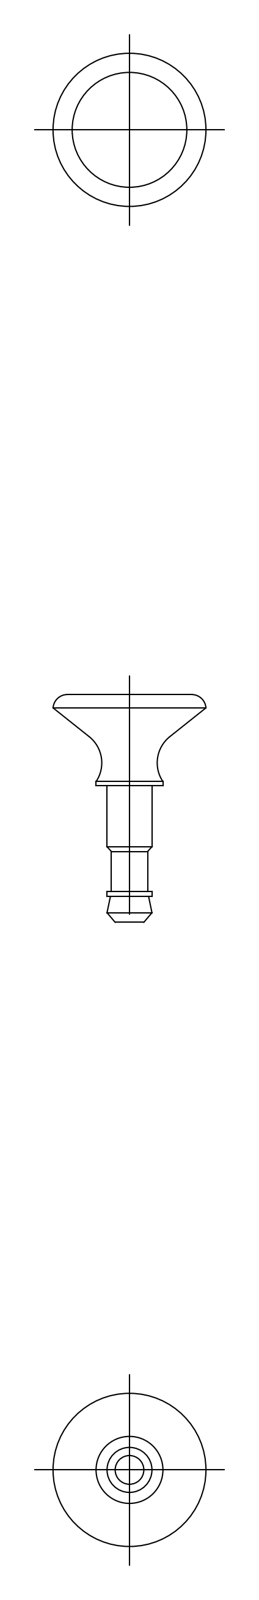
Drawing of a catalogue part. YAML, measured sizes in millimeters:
part_name: "plunger"
step_written_by: "CADfix (AUTOMOTIVE_DESIGN)"
units: millimeters
bodies: {solids: 1, faces: 26, planar: 0, cylindrical: 0, other: 26}
overall_size: [23.8, 16, 16]
volume: 888
surface_area: 792
